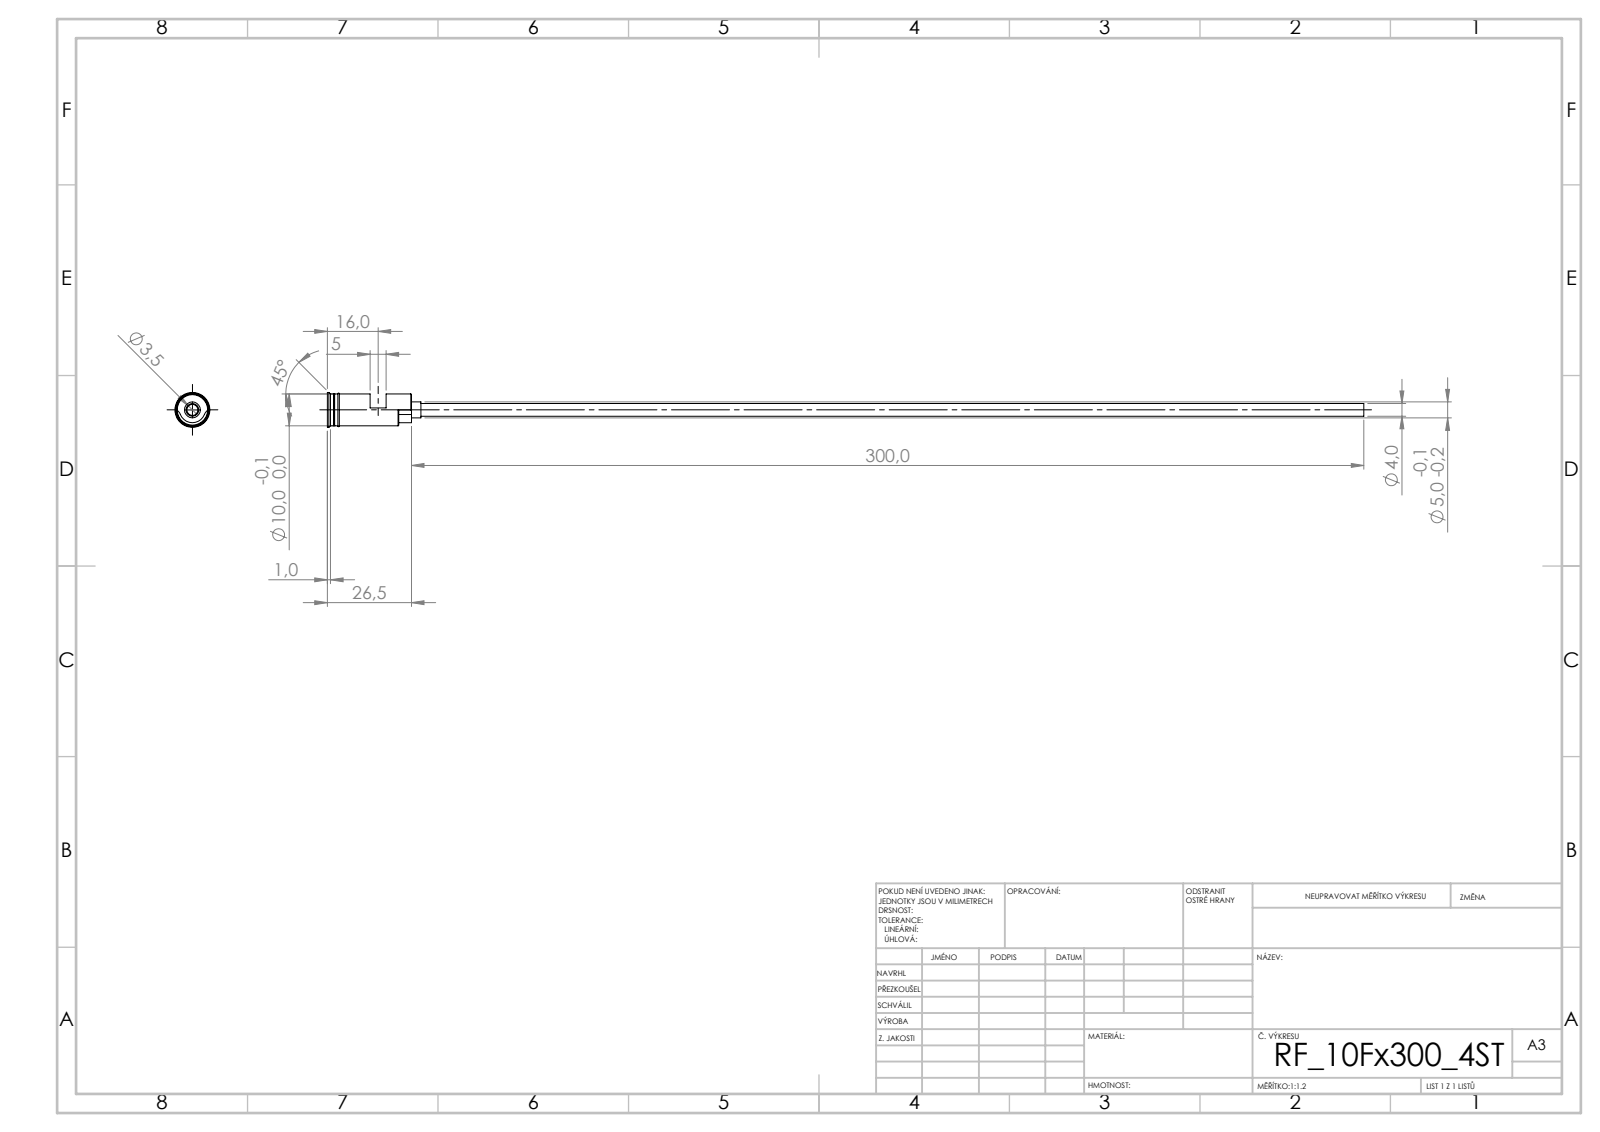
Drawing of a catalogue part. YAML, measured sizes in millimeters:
step_written_by: "SolidWorks 2019 (CONFIG_CONTROL_DESIGN)"
units: millimeters
bodies: {solids: 1, faces: 55, planar: 24, cylindrical: 19, other: 12}
overall_size: [326.5, 11, 11]
volume: 2610
surface_area: 8281
round_holes:
  - {diameter: 3.5, count: 1}
round_bosses_or_shafts:
  - {diameter: 11, count: 1}
  - {diameter: 10, count: 1}
  - {diameter: 9.8, count: 1}
  - {diameter: 5, count: 1}
  - {diameter: 4, count: 1}
partial_cylinders:
  - {radius: 3, count: 2}
  - {radius: 4.05, count: 1}
face_to_face_distances: [26.5, 13, 13.5, 24.5, 11.5, 2, 8, 5, 16.5, 18.5]
